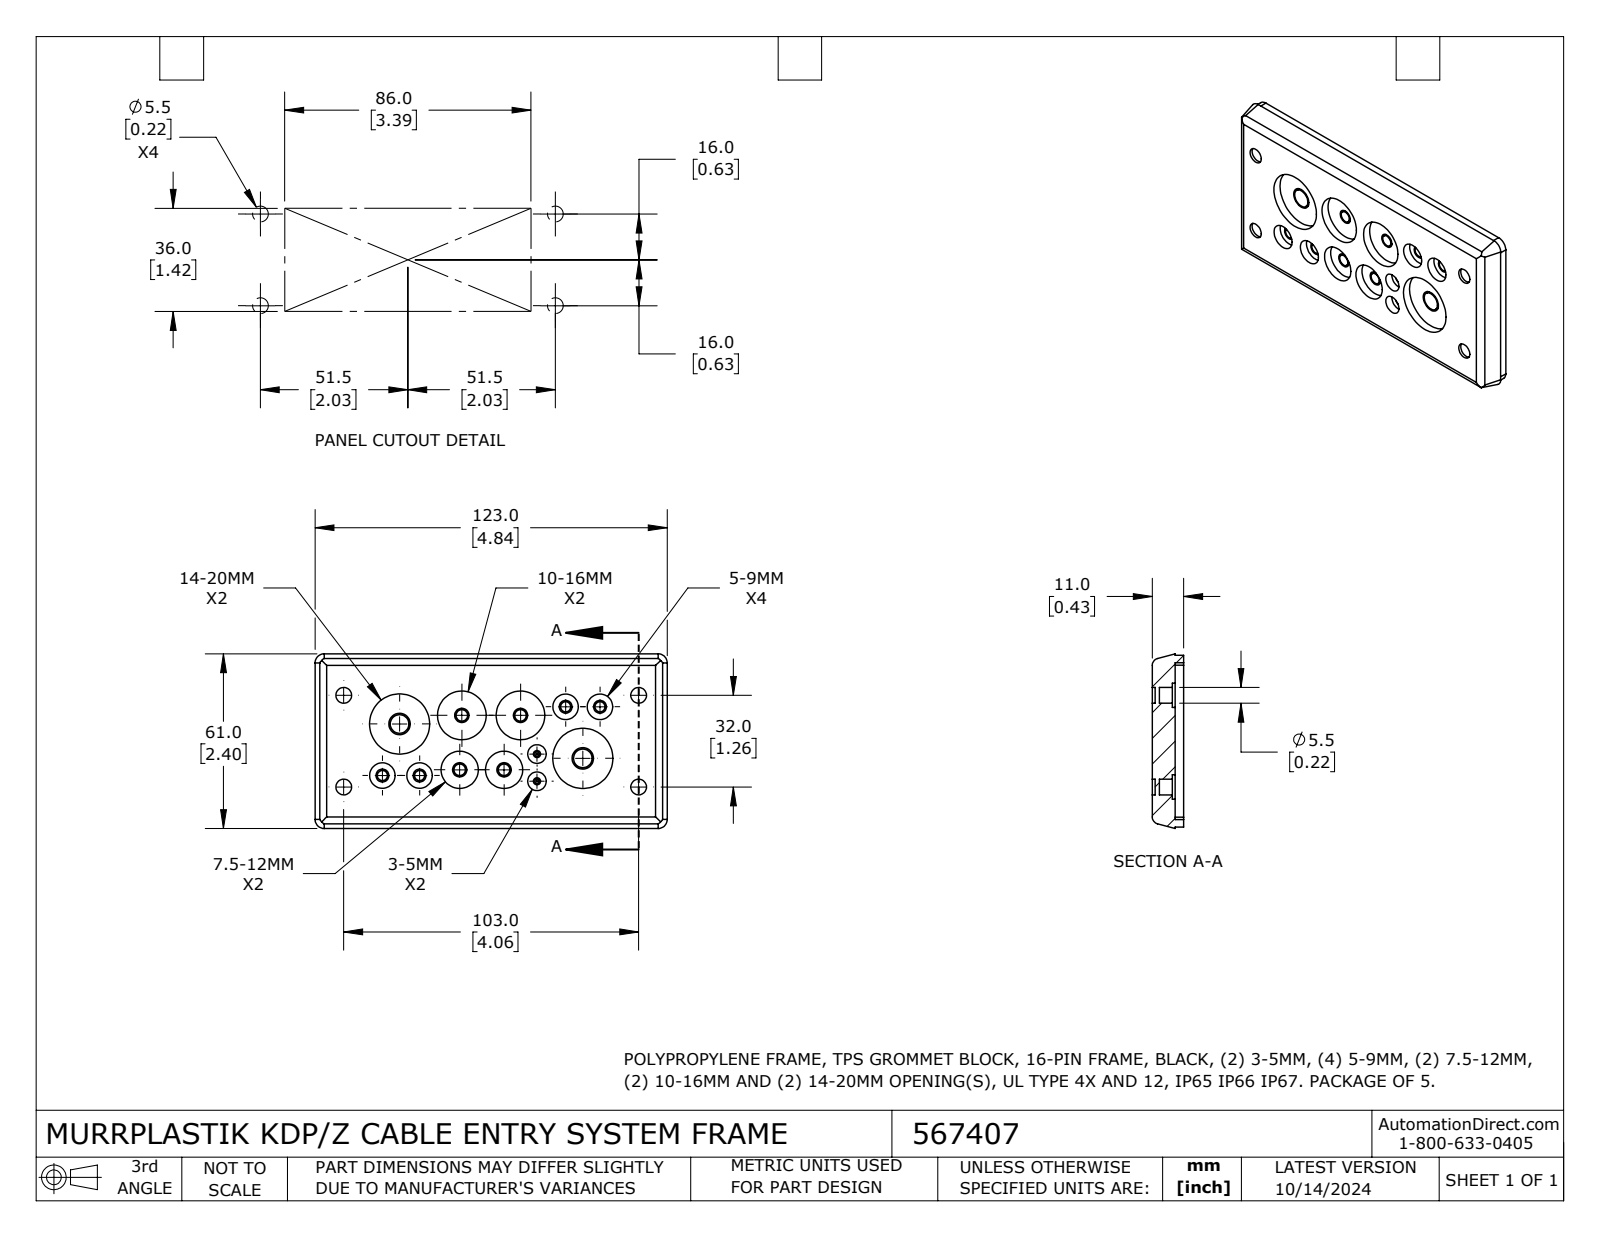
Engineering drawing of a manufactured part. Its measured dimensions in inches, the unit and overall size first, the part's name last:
Units: inches
Overall size (bounding box): 4.843 × 2.402 × 0.433
Round holes (diameter × count): ⌀0.177 ×4, ⌀0.197 ×4, ⌀0.217 ×4, ⌀0.335 ×4, ⌀0.35 ×4, ⌀0.098 ×2, ⌀0.256 ×2, ⌀0.295 ×2, ⌀0.512 ×2, ⌀0.669 ×2, ⌀0.827 ×2
Round bosses / shafts (diameter × count): ⌀0.157 ×4, ⌀0.138 ×4, ⌀0.256 ×2, ⌀0.059 ×2
Partial cylindrical surfaces — rounded edges, fillets, slot ends (radius × count): R0.012 ×8, R0.035 ×4, R0.098 ×4, R0.138 ×4, R0.244 ×4, R0.266 ×4
Main face-to-face distances: 0.217, 0.098, 0.315, 0.118, 0.197, 0.433, 0.102, 0.386, 1.976, 2.26
Hole centre spacings: 0.747, 0.554, 0.863, 1.157, 1.224, 1.26, 1.647, 1.899
Volume: 2.611 in³ · Surface area: 36.73 in²
Bodies: 1 solid, 208 faces (78 planar, 126 cylindrical, 4 other)
Part name (STEP PRODUCT): 567407
STEP written by: SolidWorks 2023 (CONFIG_CONTROL_DESIGN)
